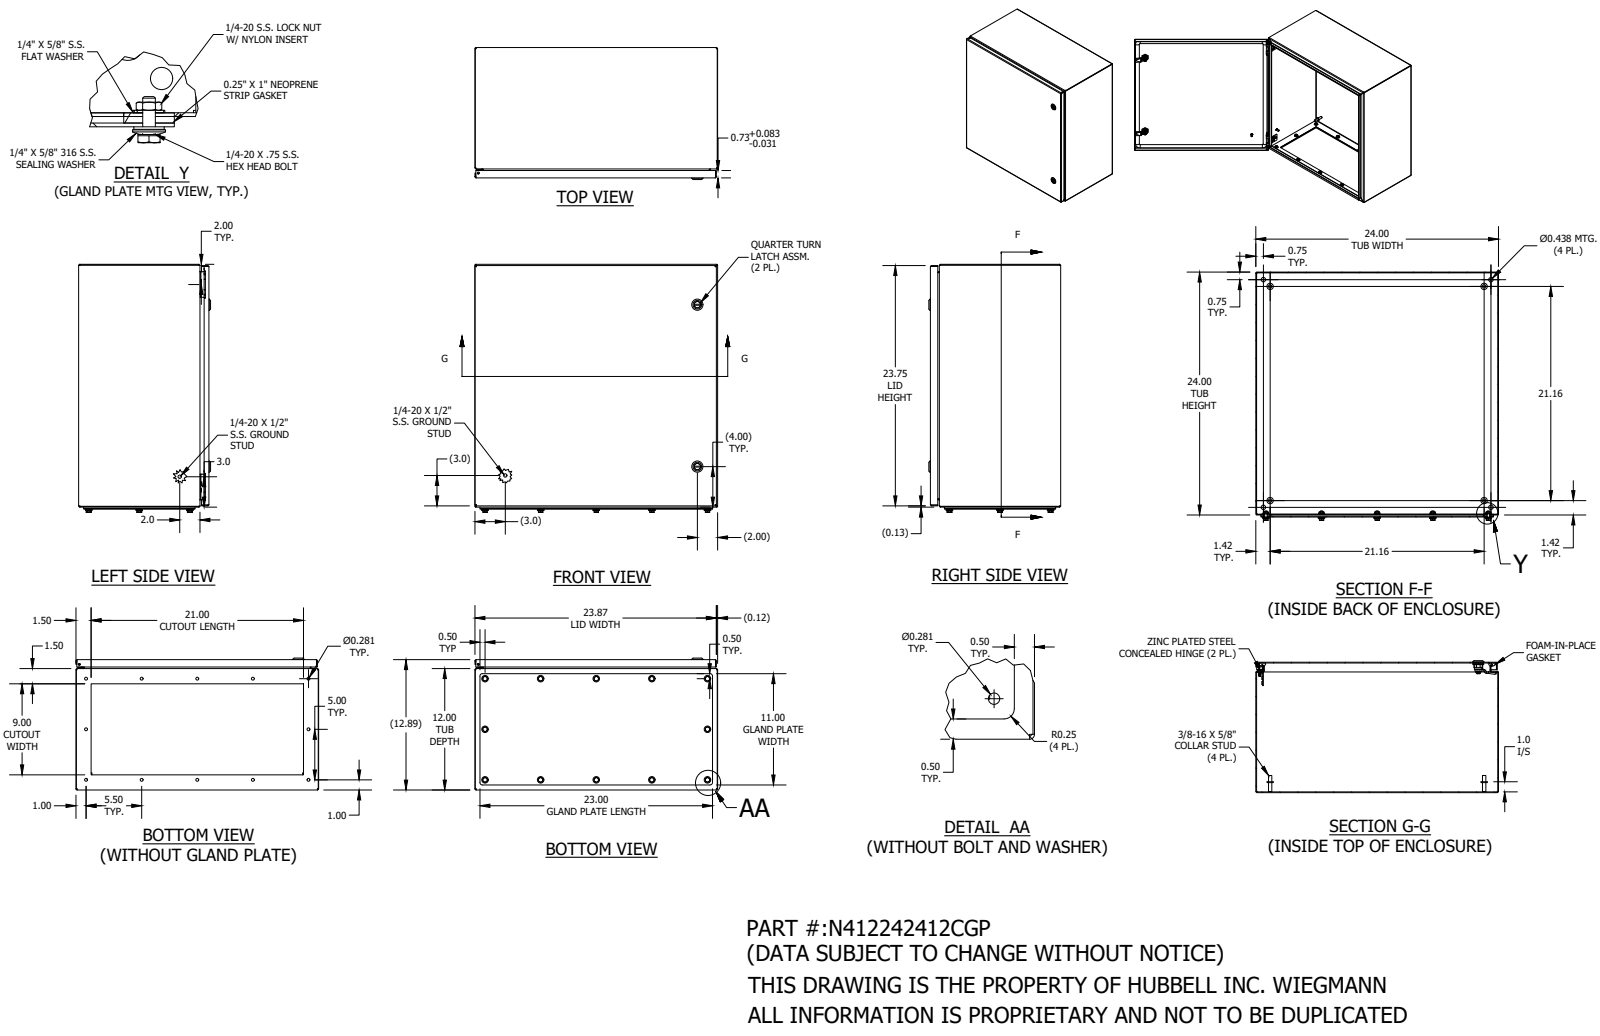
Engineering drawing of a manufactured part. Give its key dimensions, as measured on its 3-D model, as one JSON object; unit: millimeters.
{"part_name": "N412242412CGP", "step_written_by": "SolidWorks 2019 (AUTOMOTIVE_DESIGN)", "units": "millimeters", "bodies": {"solids": 95, "faces": 2687, "planar": 1101, "cylindrical": 810, "other": 776}, "overall_size": [622.8, 609.6, 331.3], "volume_mm3": 3602000, "surface_area_mm2": 3554000, "round_holes": [[7.1, 14], [5.4, 12], [7.4, 12], [4.1, 8], [7, 7], [6, 6], [6, 6], [8.9, 6], [4.8, 5], [7, 5], [2.4, 4], [4.2, 4]], "round_bosses_or_shafts": [[6.4, 22], [15.9, 13], [16.5, 12], [15.2, 12], [11.1, 12], [9.1, 4], [8.4, 4], [8.1, 4]], "partial_cylinders_radius": [[0.3, 56], [1.3, 26], [0.5, 21], [1.2, 20], [3.1, 20], [4, 9], [3.2, 8], [3.3, 8]], "face_to_face_distances": [1.9, 325.4, 1.9, 607.7, 323.5, 327.3, 612.9, 605.8, 611, 609.6], "hole_center_spacings": [127, 139.7, 254, 279.4, 289.9, 573, 558.8, 16.8]}
